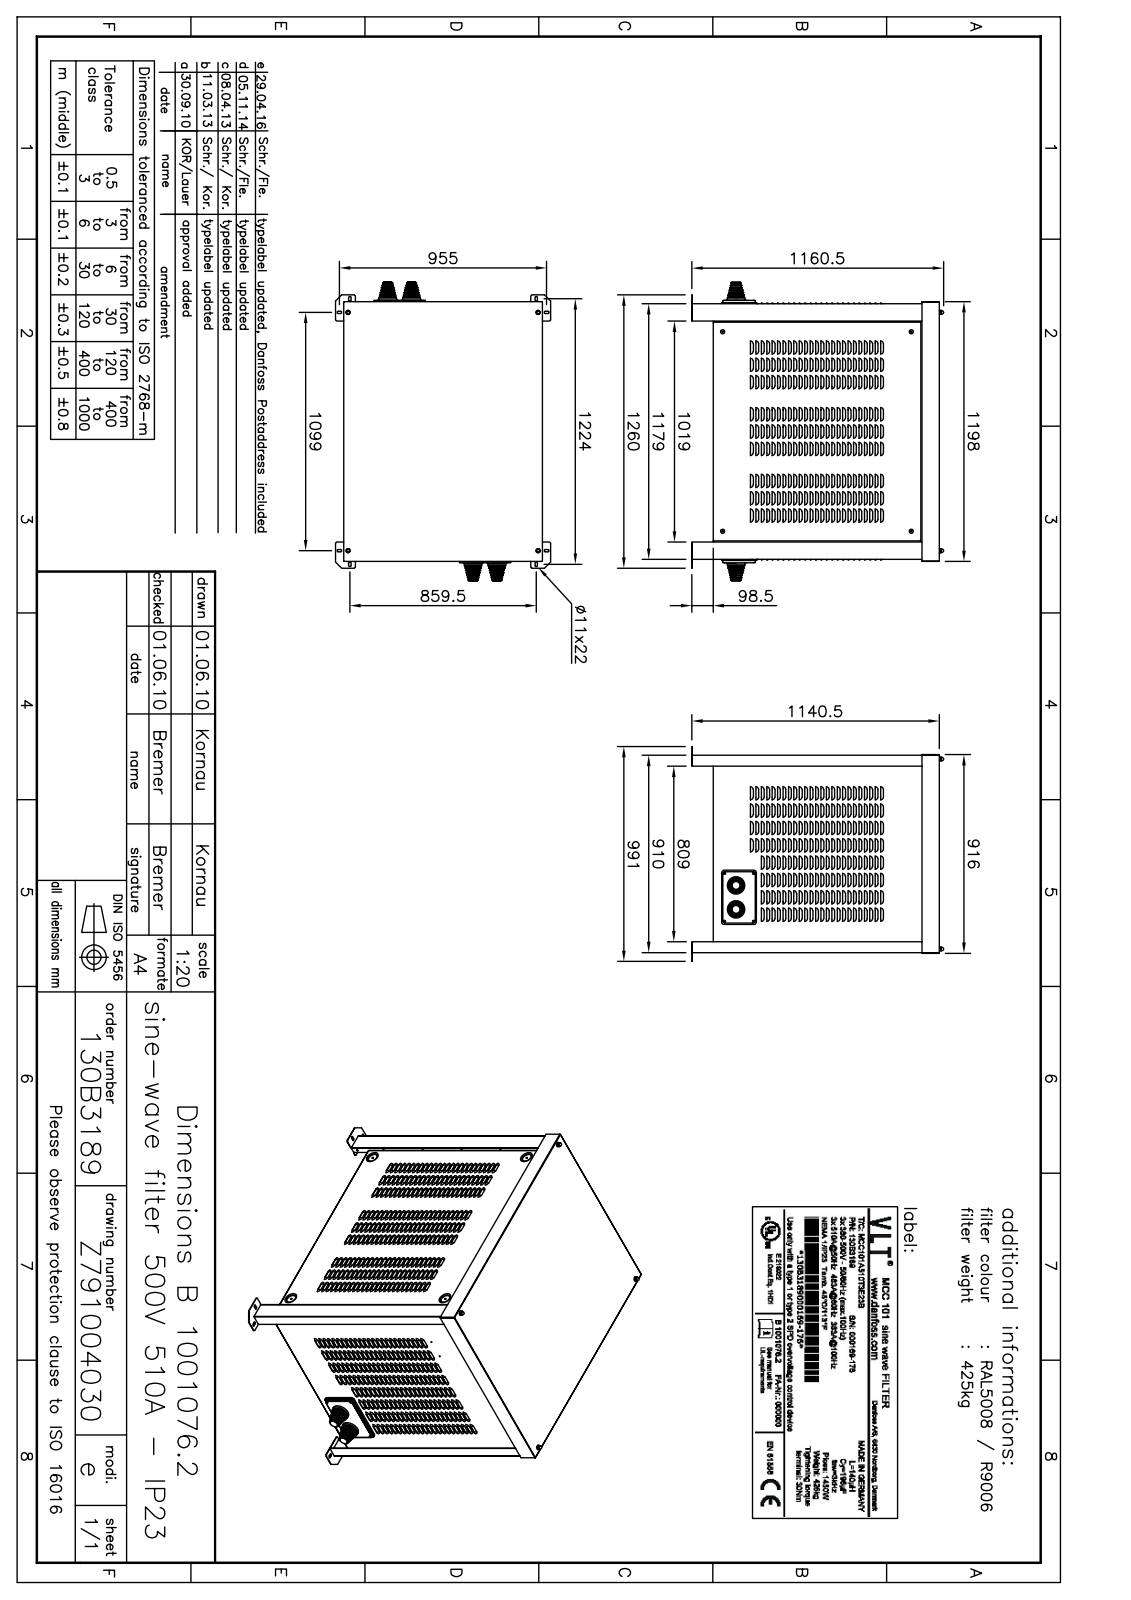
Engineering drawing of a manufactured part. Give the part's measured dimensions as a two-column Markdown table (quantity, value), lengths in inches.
| quantity | value |
| --- | --- |
| part name | +3810-0160; #700-1359; +1029-0022_Deckel; #020-1359 (+8 more) |
| STEP written by | SolidWorks 2014 (AUTOMOTIVE_DESIGN) |
| units | inches |
| bodies | 172 solids, 15735 faces (7808 planar, 3893 cylindrical, 4034 other) |
| overall size | 54.291 × 45.709 × 39.035 |
| volume | 4 045 in³ |
| surface area | 39 800 in² |
| round holes (diameter × count) | 0.512 × 34, 0.217 × 29, 0.413 × 20, 0.335 × 19, 0.165 × 18, 0.433 × 16, 0.394 × 14, 0.256 × 13, 0.13 × 10, 0.15 × 10, 0.591 × 10, 0.28 × 9 |
| round bosses / shafts (diameter × count) | 0.236 × 16, 0.787 × 14, 0.591 × 12, 0.276 × 8, 2.559 × 6, 2.181 × 6, 0.669 × 5, 0.472 × 5 |
| partial cylindrical surfaces (radius × count) | 0.197 × 516, 0.472 × 100, 0.551 × 75, 0.004 × 57, 0.083 × 44, 0.036 × 36, 0.157 × 34, 0.039 × 30 |
| main face-to-face distances | 0.079, 0.118, 34.311, 46.142, 0.748, 1.575, 0.689, 34.39, 0.827, 40.669 |
| hole center spacings | 8.661, 12.303, 19.685, 25.197, 35.903, 2.461, 6.299, 15.728 |
